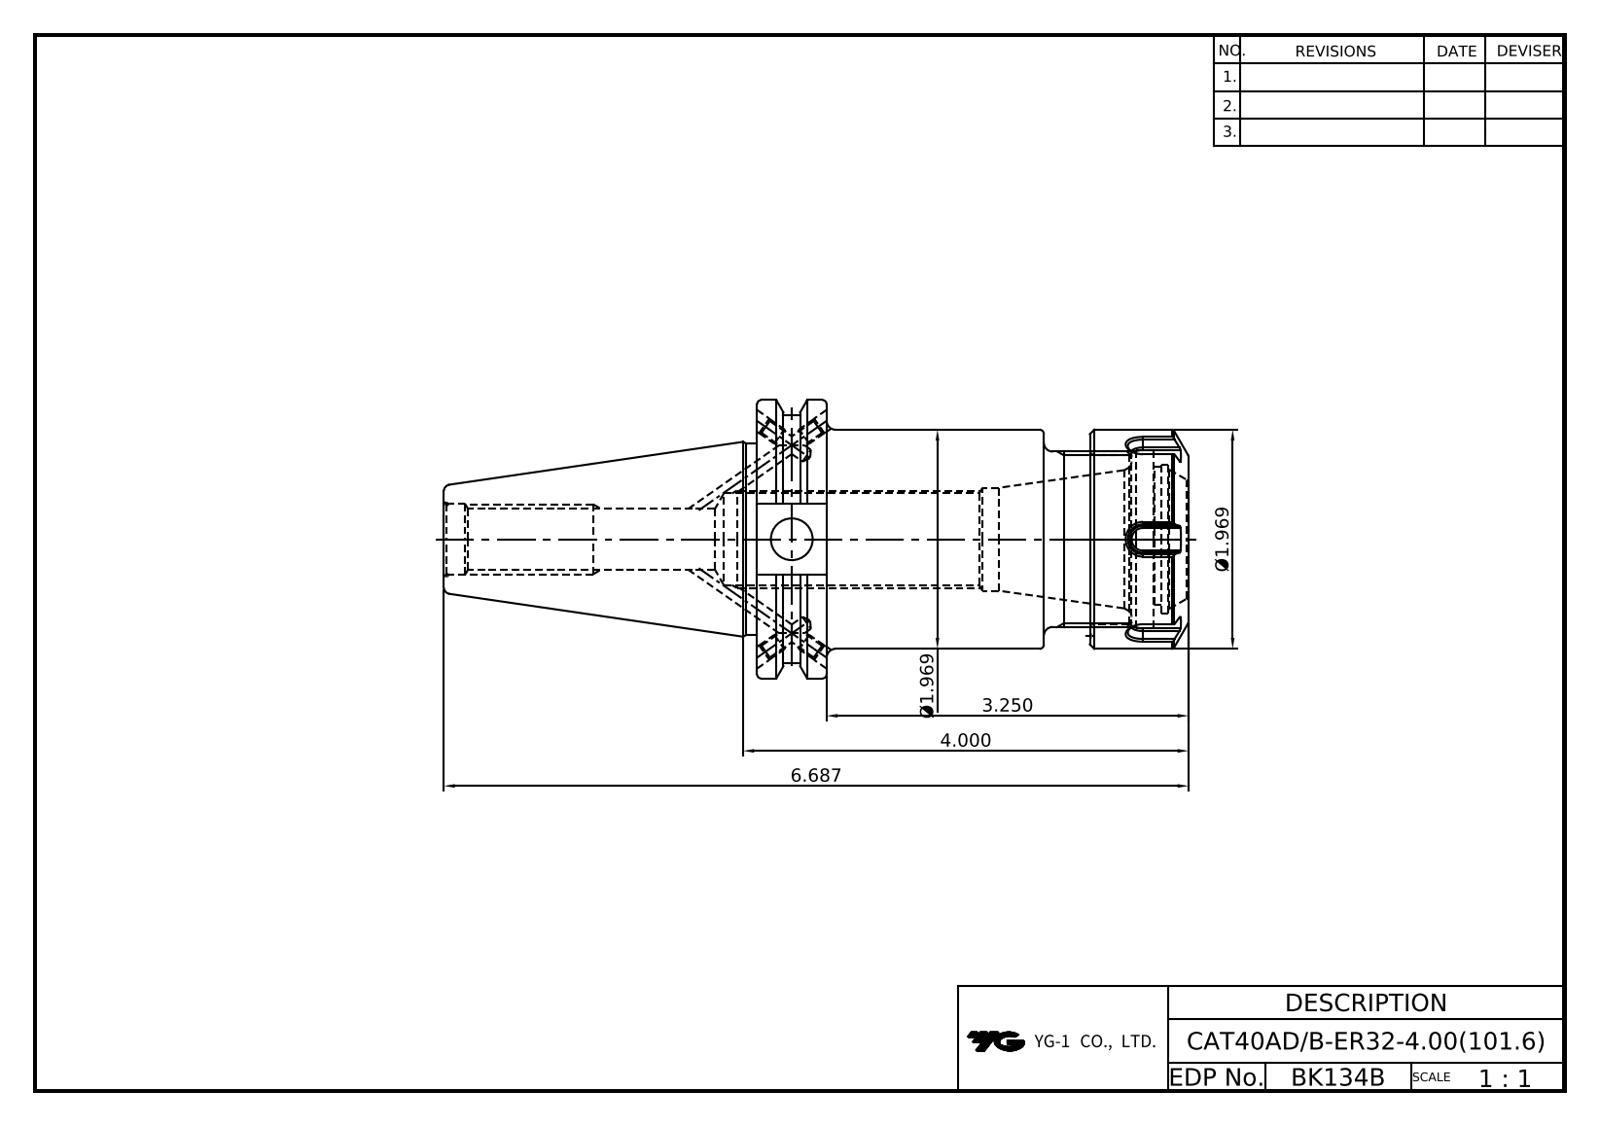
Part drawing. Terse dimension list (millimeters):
name: LO-CAT40ADB-ER32-4.00; ER32NUT
written by: Autodesk Inventor 2024 (AUTOMOTIVE_DESIGN)
unit: mm
bodies: 2 solids, 171 faces (71 planar, 46 cylindrical, 54 other)
size: 169.85 × 63.5 × 61.09
volume: 203 902 mm³; area: 44 978 mm²
holes: 4× ⌀3.24, 4× ⌀4, 1× ⌀1, 1× ⌀9.53, 1× ⌀13.39, 1× ⌀16.3, 1× ⌀20.5, 1× ⌀23.5, 1× ⌀27.1, 1× ⌀31.4, 1× ⌀33.8, 1× ⌀38.6
bosses: 1× ⌀63.5, 1× ⌀56.3, 1× ⌀50, 1× ⌀43.6, 1× ⌀40
rounds: 12× R0.5, 1× R8.19
face distances: 98.43, 75.93, 22.5, 15.88, 60.05, 82.55, 90.53, 74.65, 14.6, 7.9
hole spacings: 35.13, 0.48, 0.74, 0.8, 22, 22.2, 22.8
